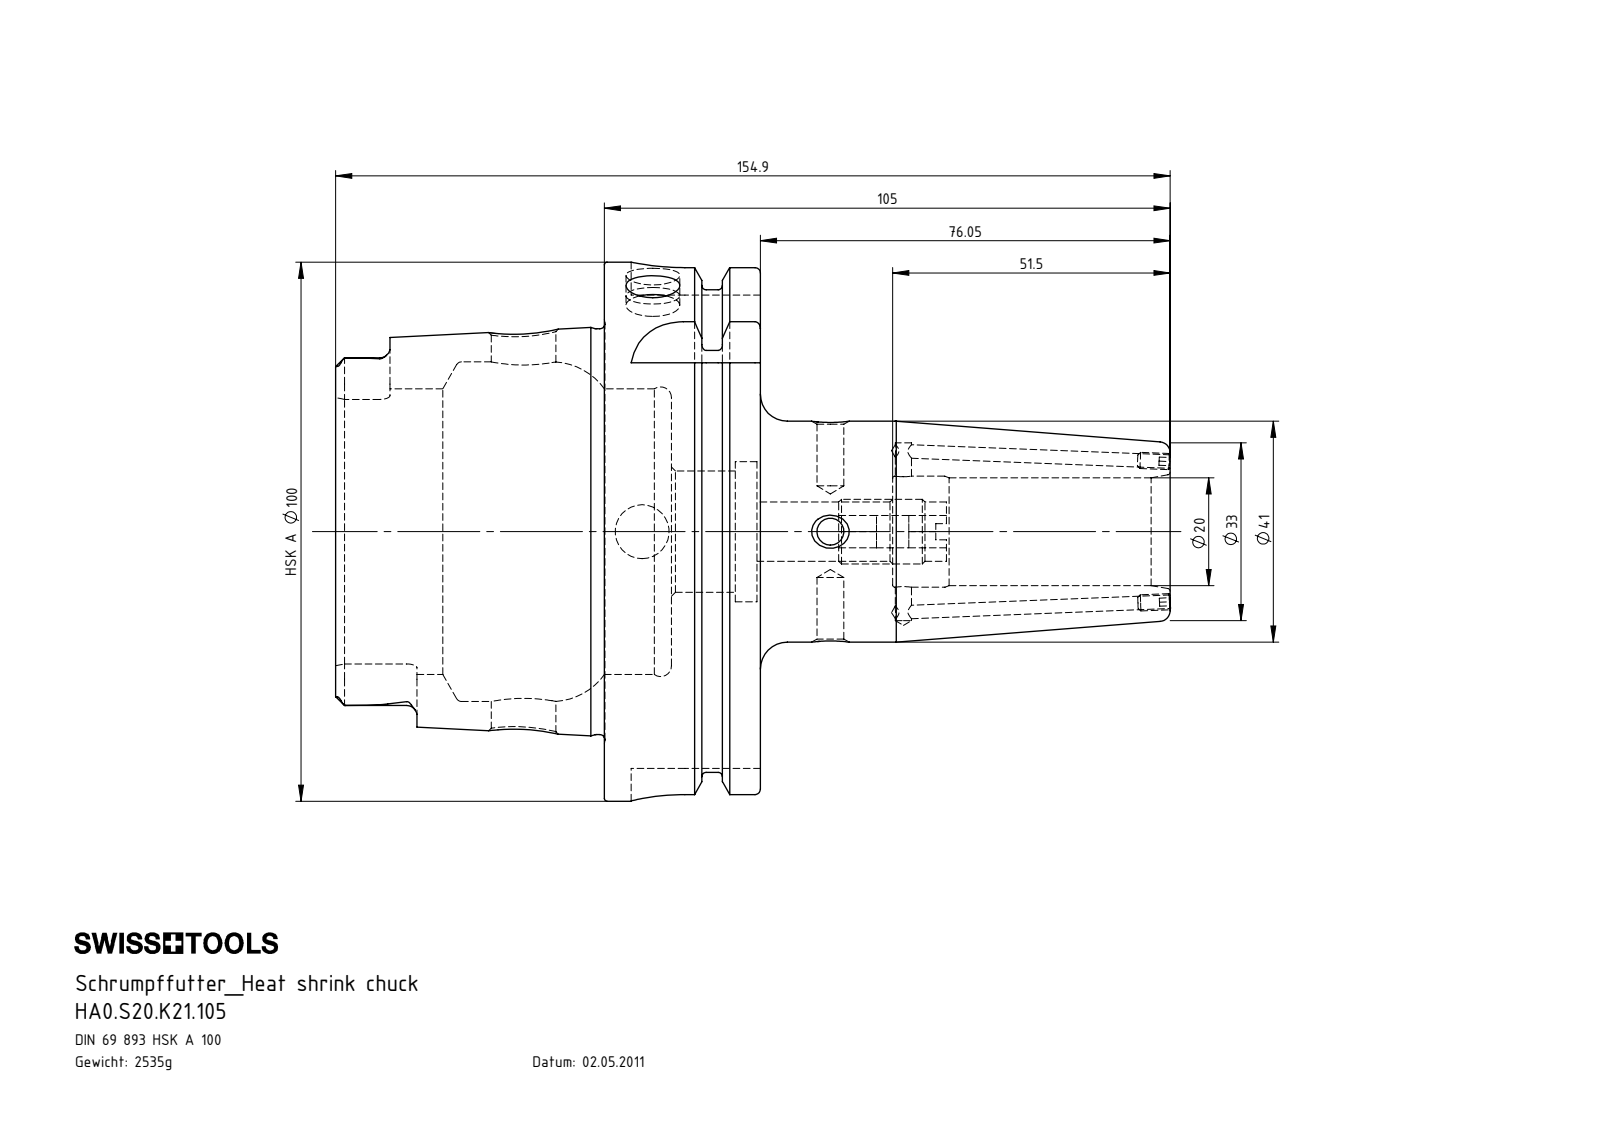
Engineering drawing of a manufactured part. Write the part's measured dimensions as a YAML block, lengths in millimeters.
part_name: "ERU-CJ2.001.006; ERU-AN5.K01.020_A; HA0.S20.K21.105; HA0-S20.K21.105_C_Fertigbearbeitung"
step_written_by: "SolidWorks 2017 (AUTOMOTIVE_DESIGN)"
units: millimeters
bodies: {solids: 4, faces: 296, planar: 95, cylindrical: 85, other: 116}
overall_size: [154.98, 100, 100]
volume: 322904
surface_area: 65174
round_holes:
  - {diameter: 10, count: 3}
  - {diameter: 2.5, count: 2}
  - {diameter: 5, count: 2}
  - {diameter: 3, count: 1}
  - {diameter: 6, count: 1}
  - {diameter: 11, count: 1}
  - {diameter: 12, count: 1}
  - {diameter: 20, count: 1}
  - {diameter: 20.6, count: 1}
  - {diameter: 22.5, count: 1}
  - {diameter: 26, count: 1}
  - {diameter: 53, count: 1}
round_bosses_or_shafts:
  - {diameter: 3, count: 2}
  - {diameter: 100, count: 1}
  - {diameter: 91.95, count: 1}
  - {diameter: 75.26, count: 1}
  - {diameter: 41, count: 1}
  - {diameter: 12, count: 1}
partial_cylinders:
  - {radius: 1.9, count: 6}
  - {radius: 4.88, count: 4}
  - {radius: 10, count: 4}
face_to_face_distances: [28.95, 12.45, 16.5, 49.9, 62.35, 78.85, 87.8, 78.2, 28.3, 15.85]
hole_center_spacings: [13.55, 34.95, 56.95, 70.5]
